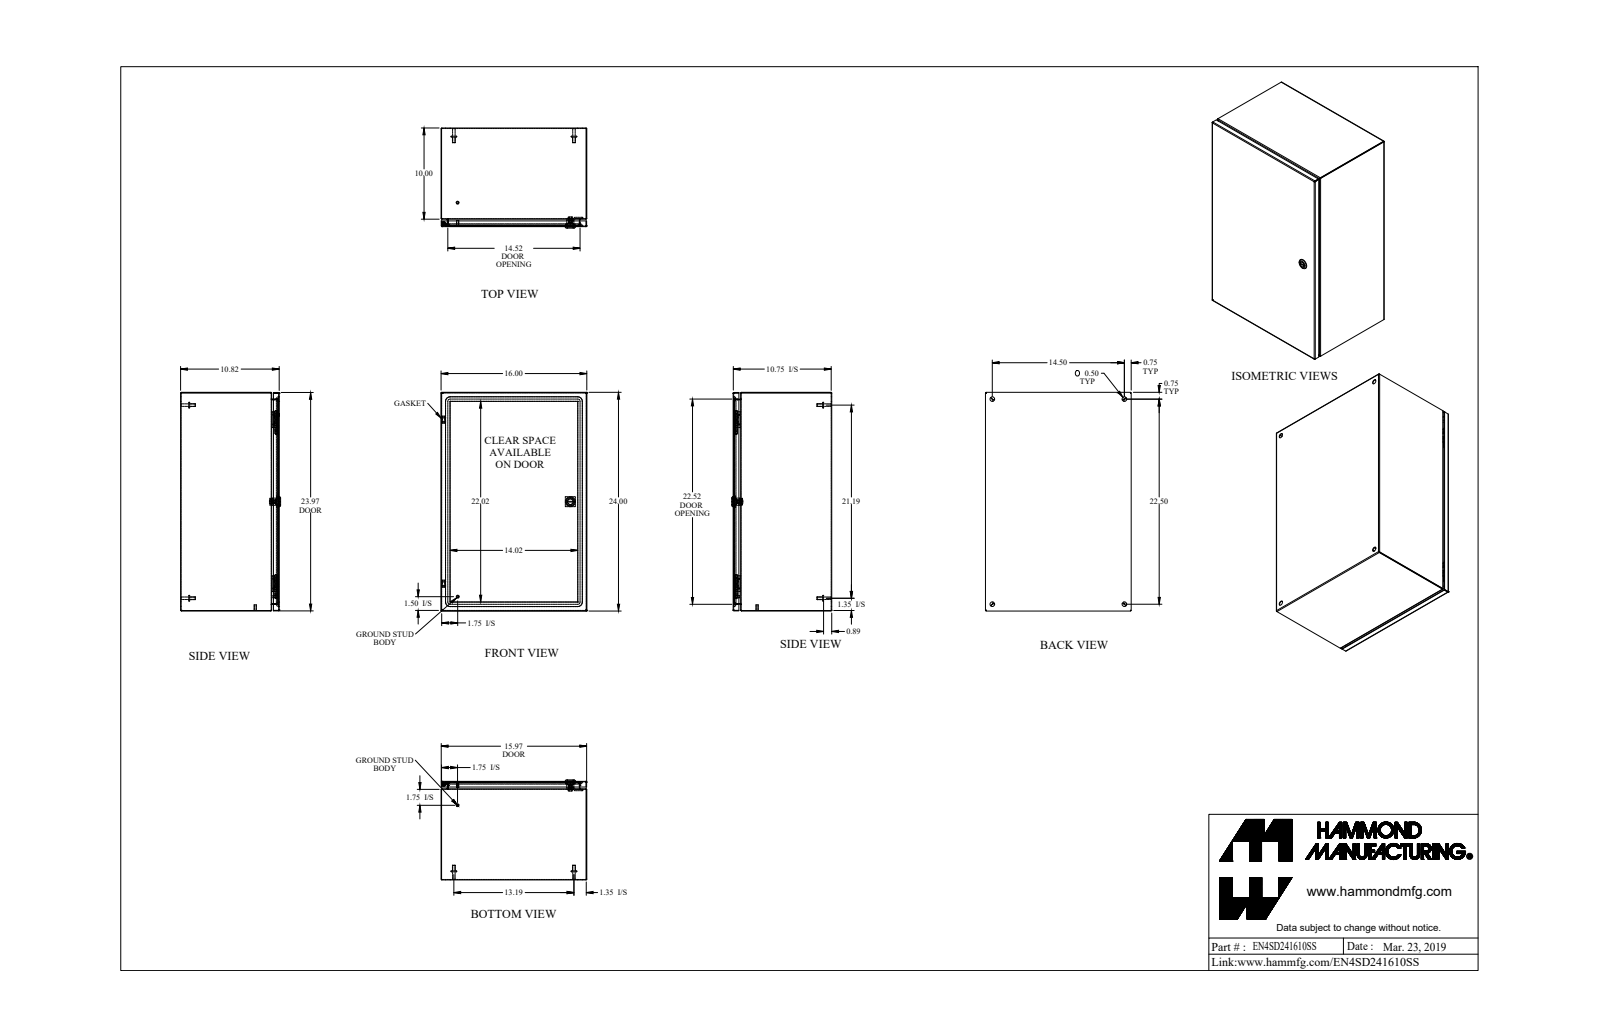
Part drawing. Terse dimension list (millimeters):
name: EN4SD241610SS_Default
written by: SolidWorks 2019 (CONFIG_CONTROL_DESIGN)
unit: mm
bodies: 22 solids, 657 faces (303 planar, 212 cylindrical, 142 other)
size: 609.6 × 406.4 × 278.9
volume: 1 739 000 mm³; area: 2 340 000 mm²
holes: 5× ⌀12.7, 1× ⌀4.4, 1× ⌀5, 1× ⌀6.1, 1× ⌀6.1, 1× ⌀9.8, 1× ⌀16, 1× ⌀19.5
bosses: 6× ⌀8, 4× ⌀15.9, 4× ⌀7, 2× ⌀6.4, 1× ⌀27.9, 1× ⌀19.9, 1× ⌀15.9, 1× ⌀13.3
rounds: 21× R0.7, 21× R2.2, 12× R4.8, 4× R0.2, 4× R1.6, 4× R6.4, 4× R12.7, 2× R3.2
face distances: 1.4, 273.4, 405, 272, 274.9, 608.2, 403.5, 406.4, 606.7, 609.6
hole spacings: 287, 368.3, 445.2, 571.5, 679.9
